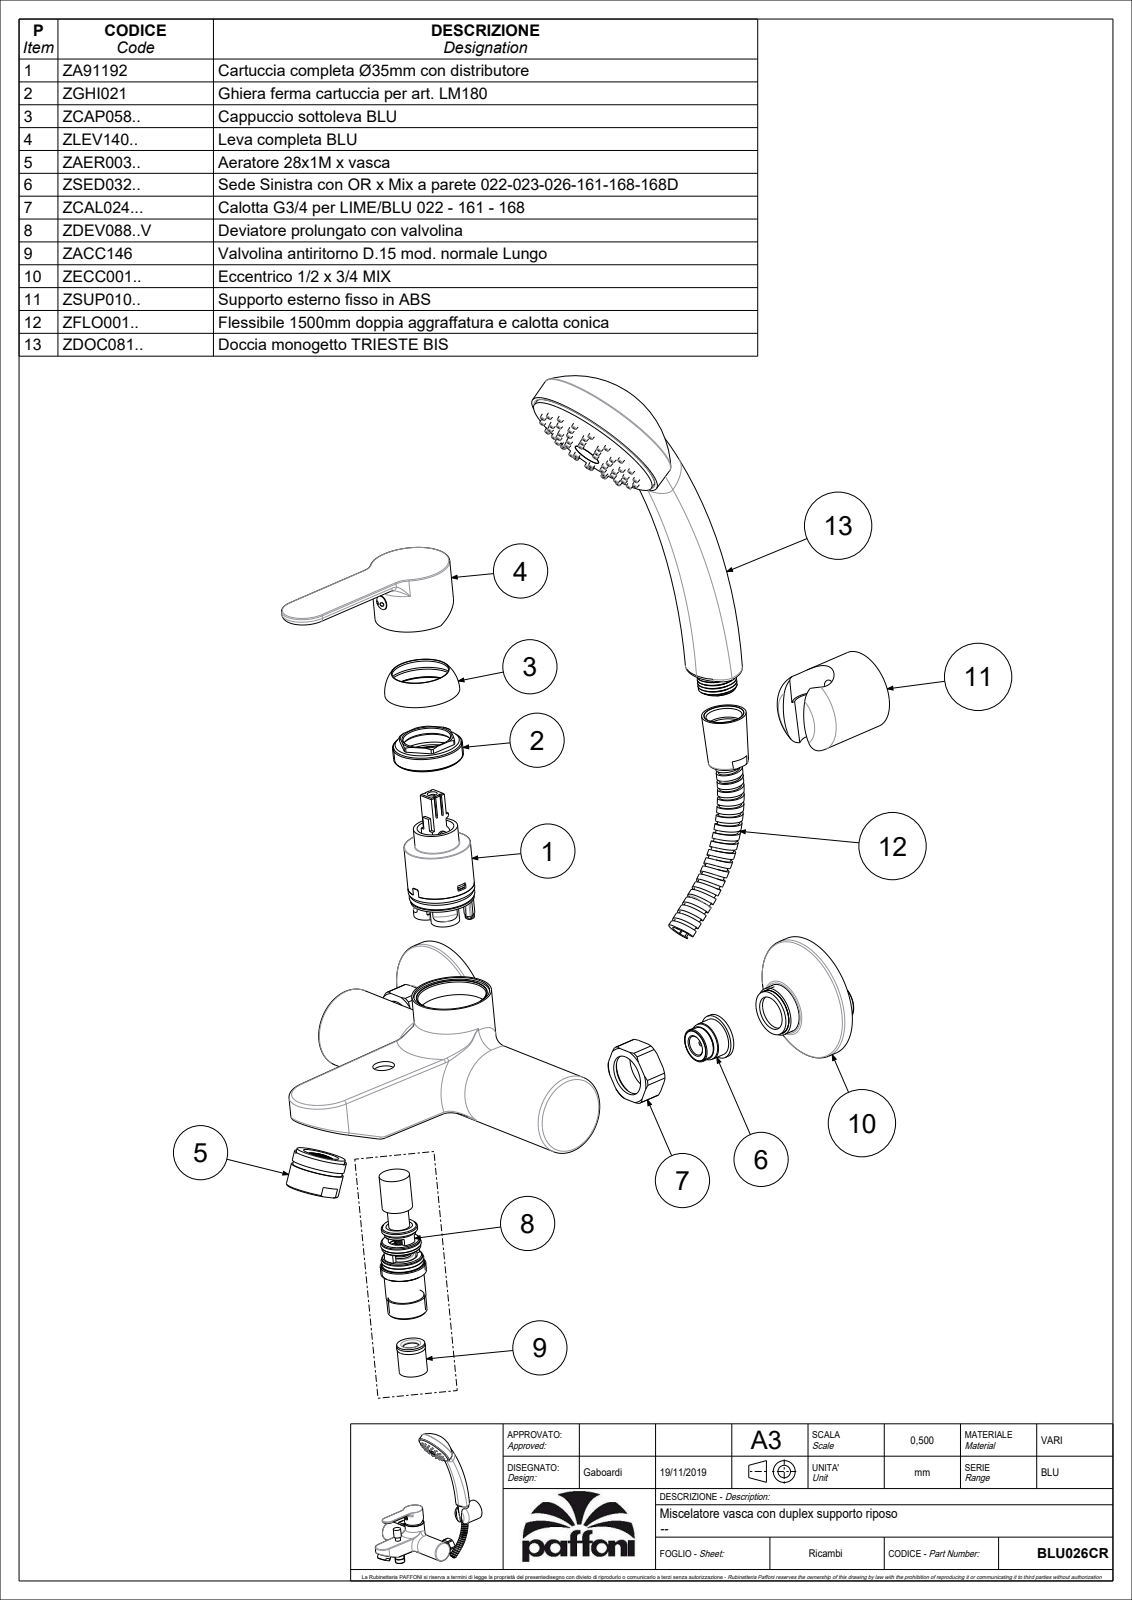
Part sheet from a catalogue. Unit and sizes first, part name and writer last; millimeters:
Units: millimetres
Overall size (bounding box): 322.9 × 296.5 × 166.2
Round holes (diameter × count): ⌀1.5 ×48, ⌀5 ×5, ⌀12 ×3, ⌀17 ×3, ⌀18 ×3, ⌀38 ×3, ⌀7 ×2, ⌀8 ×2, ⌀9.5 ×2, ⌀16.3 ×2, ⌀20 ×2, ⌀21.5 ×2
Round bosses / shafts (diameter × count): ⌀3 ×48, ⌀42 ×3, ⌀20.8 ×3, ⌀20.5 ×3, ⌀65.5 ×2, ⌀28.32 ×2, ⌀26.2 ×2, ⌀25 ×2
Partial cylindrical surfaces — rounded edges, fillets, slot ends (radius × count): R0.5 ×37, R1 ×11, R1.5 ×11, R1.2 ×9, R0.3 ×6, R2 ×6, R6 ×4, R10 ×3
Main face-to-face distances: 2, 69, 109, 20, 67, 20.5, 111, 178, 7.5, 5.5
Hole centre spacings: 29.7, 15, 10.43, 16.07, 24.57, 8.19, 28.44, 31.34
Volume: 398 984 mm³ · Surface area: 218 514 mm²
Bodies: 3 solids, 3087 faces (2055 planar, 627 cylindrical, 405 other)
Part name (STEP PRODUCT): BLU026CR
STEP written by: CREO PARAMETRIC BY PTC INC, 2020044 (CONFIG_CONTROL_DESIGN)
